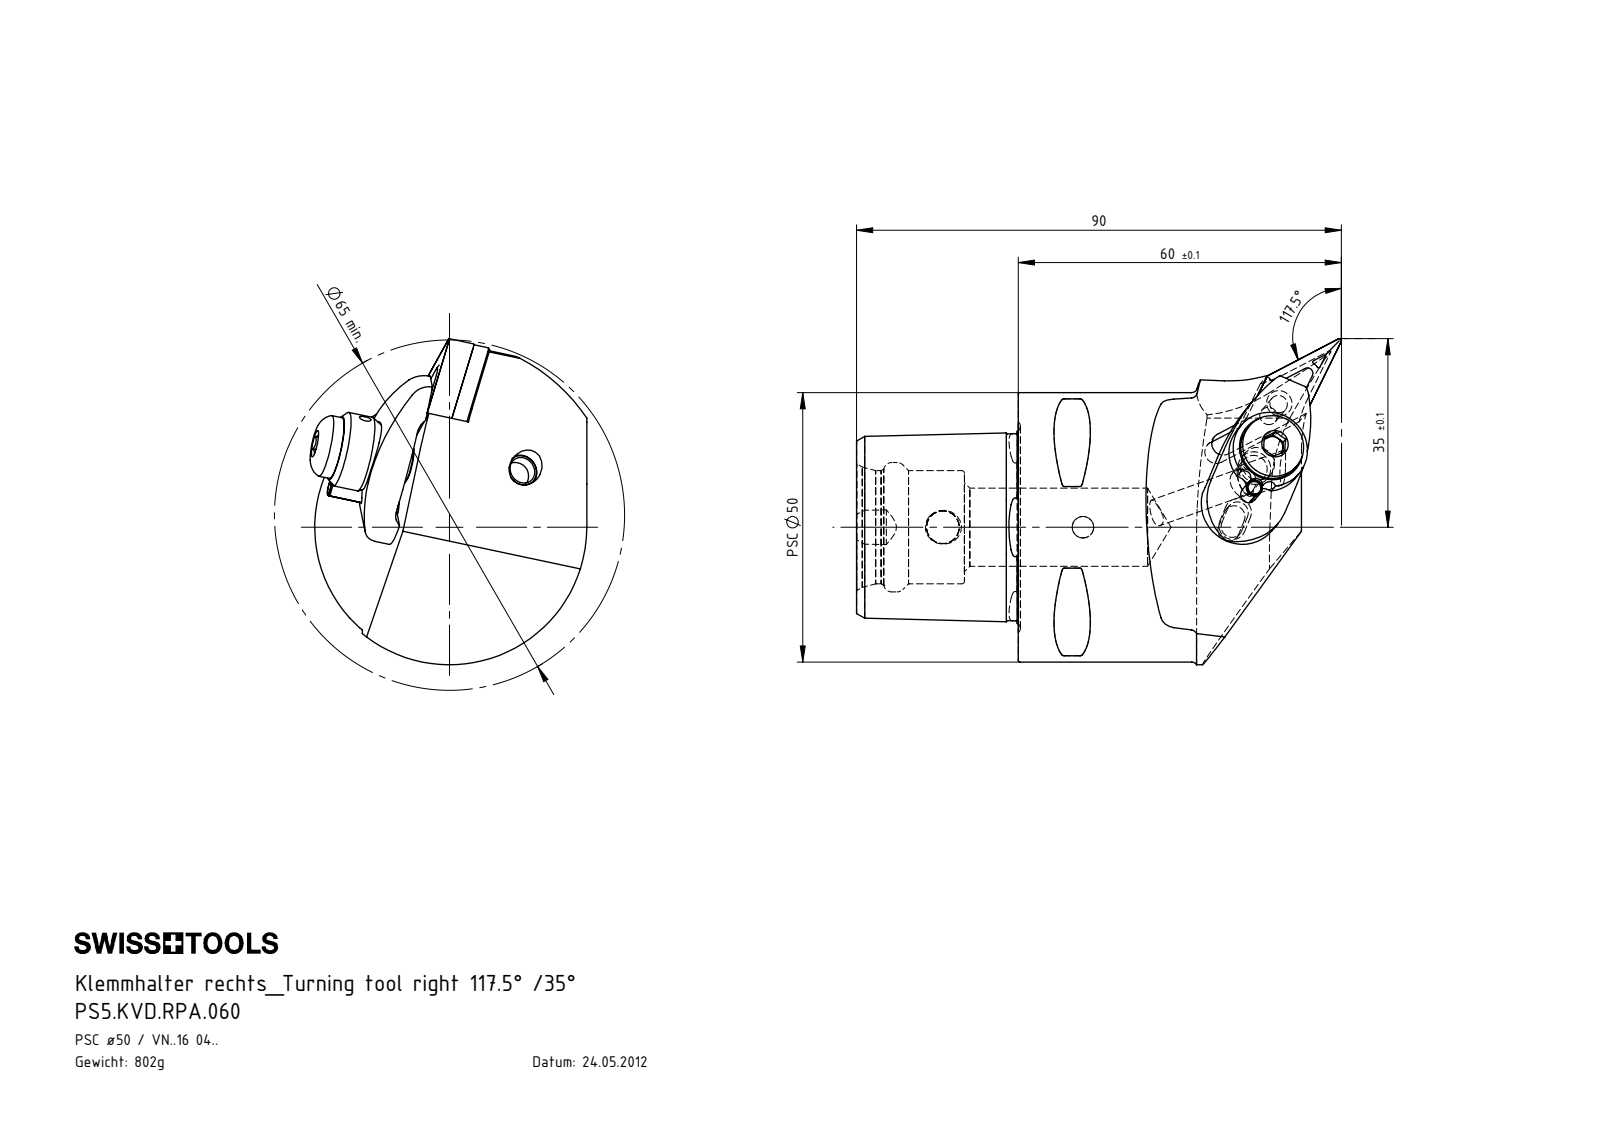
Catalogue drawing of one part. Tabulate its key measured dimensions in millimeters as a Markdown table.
| quantity | value |
| --- | --- |
| part name | WCC-ER5.102.012_B; WCC-ER3.102.024_C; VNMG160404; WCB-ER2.001.009_A (+7 more) |
| STEP written by | SolidWorks 2012 (CONFIG_CONTROL_DESIGN) |
| units | millimeters |
| bodies | 11 solids, 434 faces (100 planar, 133 cylindrical, 201 other) |
| overall size | 90 × 60.5 × 51.34 |
| volume | 101 617 mm³ |
| surface area | 24 200 mm² |
| round holes (diameter × count) | 2 × 3, 5 × 3, 7 × 2, 2.4 × 1, 3 × 1, 3.3 × 1, 3.8 × 1, 4 × 1, 4.95 × 1, 6 × 1, 6.1 × 1, 6.2 × 1 |
| round bosses / shafts (diameter × count) | 6 × 2, 4 × 2, 3 × 2, 50 × 1, 14 × 1, 11.5 × 1, 6.8 × 1, 6.2 × 1 |
| partial cylindrical surfaces (radius × count) | 0.5 × 10, 0.34 × 6, 0.59 × 6, 0.4 × 4, 1.5 × 3, 3 × 3, 2 × 2, 4 × 2 |
| main face-to-face distances | 30, 7.62, 3.18, 4.44, 9.53, 1.31, 8.93, 5.75, 19.18, 9.08 |
| hole center spacings | 22.32, 8.01, 8.03, 8.19, 14.13, 14.29, 14.31, 22.33 |
